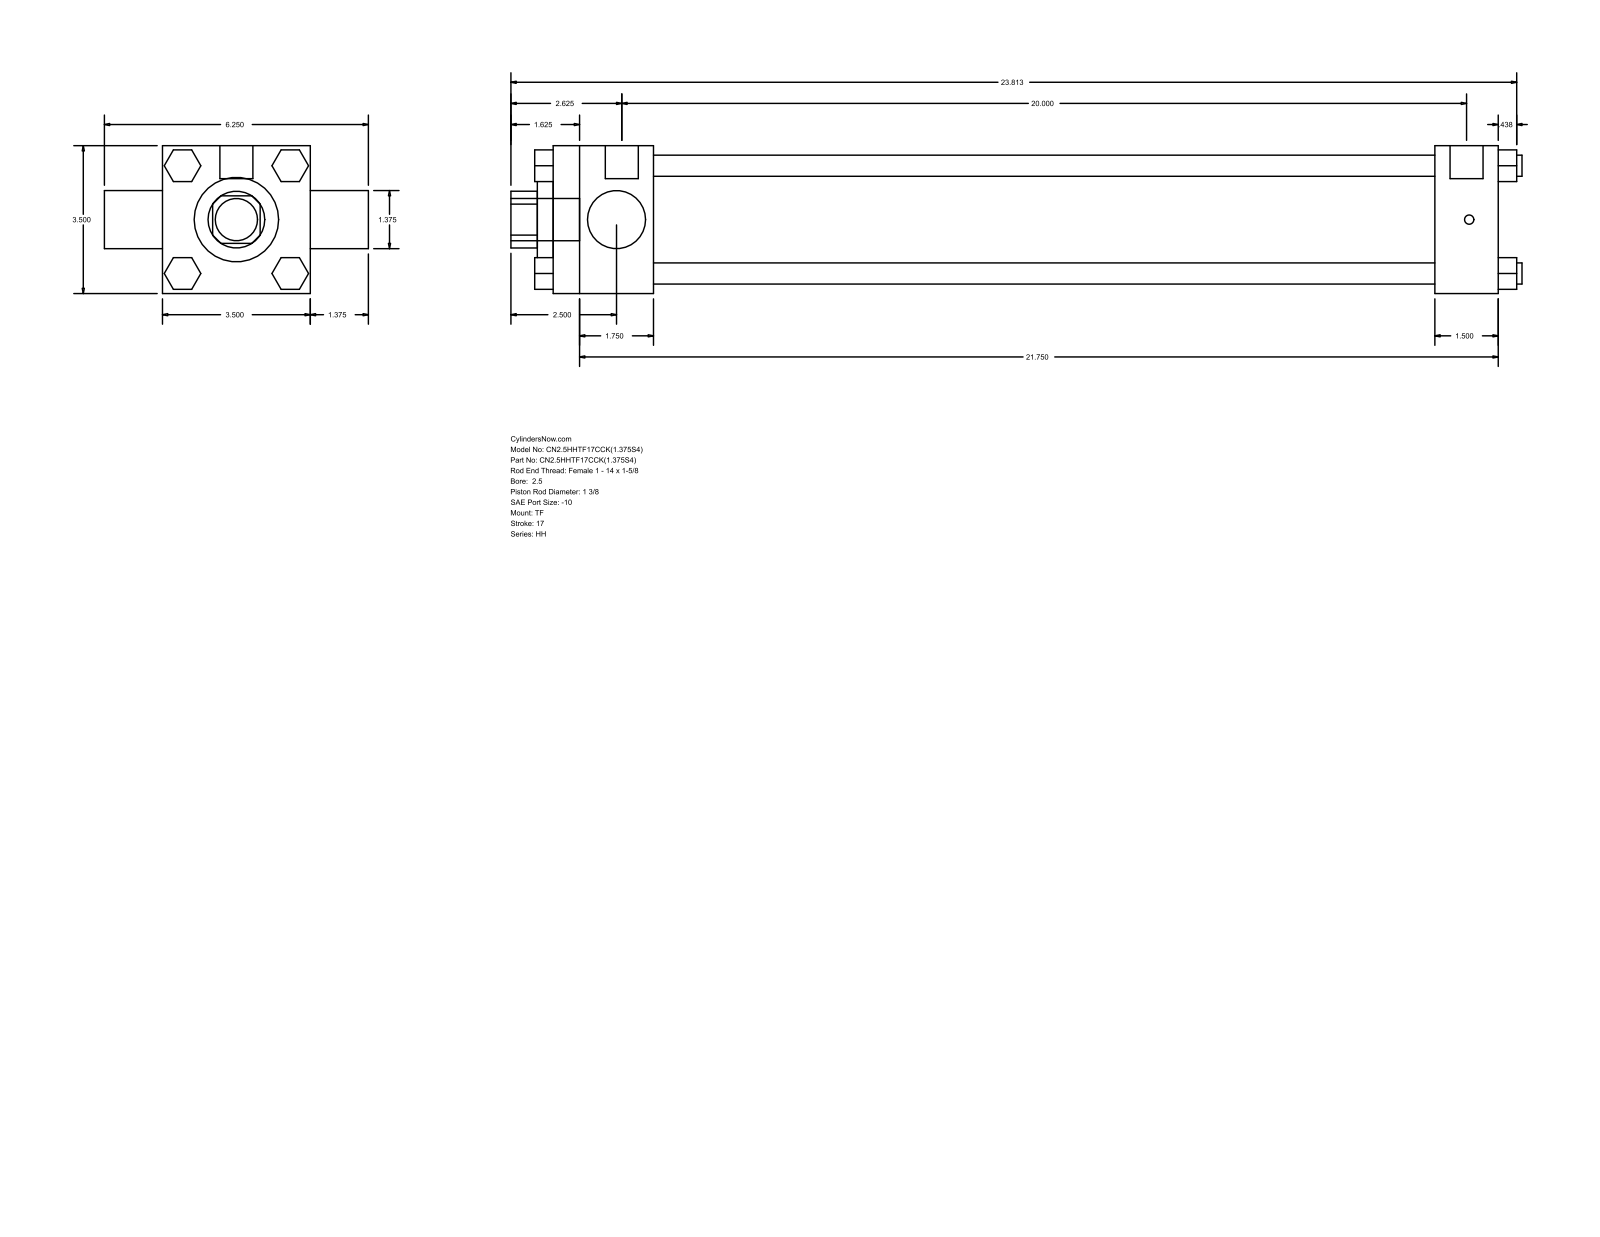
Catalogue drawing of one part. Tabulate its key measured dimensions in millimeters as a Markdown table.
| quantity | value |
| --- | --- |
| part name | HH_TF__0250_1.375 |
| STEP written by | GSSL Pune (CONFIG_CONTROL_DESIGN) |
| units | millimeters |
| bodies | 0 solids, 120 faces (92 planar, 28 cylindrical, 0 other) |
| overall size | 608.01 × 158.75 × 88.9 |
| round holes (diameter × count) | 34.92 × 2, 50.8 × 1, 73.03 × 1 |
| round bosses / shafts (diameter × count) | 12.7 × 4, 5.56 × 3, 19.84 × 2, 25.4 × 1 |
| partial cylindrical surfaces (radius × count) | 17.06 × 1 |
| main face-to-face distances | 88.9, 568.33, 60.32, 508.01, 530.22, 469.9, 38.11, 19.05, 32.38, 56.09 |
